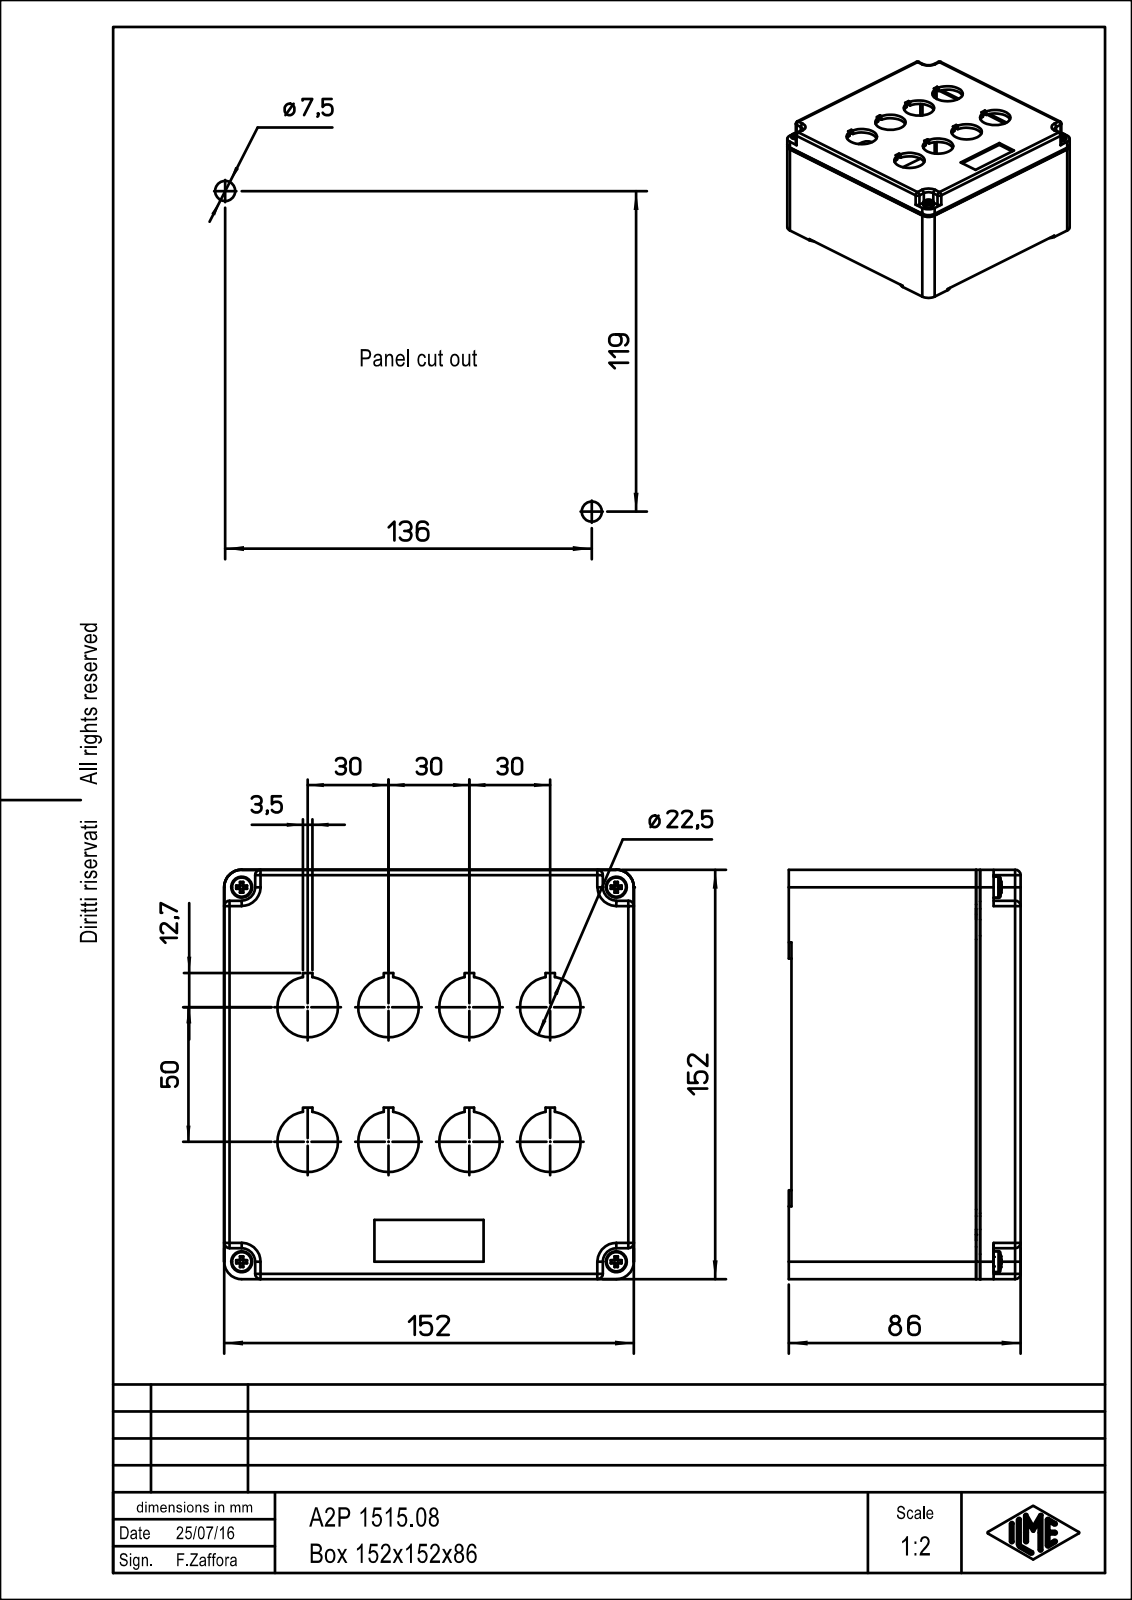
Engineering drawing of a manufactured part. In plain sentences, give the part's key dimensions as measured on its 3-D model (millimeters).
The part is named "COVER; BOX; A2P_1515.08". Its 3-D file was written by "PTC Creo Elements/Direct Modeling 19.0B 21-Mar-2015 (C) Parametric Technology GmbH (AUTOMOTIVE_DESIGN)". It is 2 solids with 1028 faces: 811 planar, 177 cylindrical and 40 other. Overall it measures 152.02 by 152 by 86 millimeters. Its volume is 382 133 cubic millimeters and its surface area 200 962 square millimeters. Round holes: 8 of diameter 22.5, 6 of diameter 3.3, 4 of diameter 4.5, 2 of diameter 5.8, 2 of diameter 7.5, 1 of diameter 10.6, 1 of diameter 10.61. Round bosses or shafts: 4 of diameter 7.8, 4 of diameter 4, 2 of diameter 6.2, 2 of diameter 6, 1 of diameter 7. Partial cylindrical surfaces (rounded edges, fillets, slot ends): 22 of radius 0.33, 17 of radius 2, 12 of radius 6, 12 of radius 6.5, 6 of radius 5, 6 of radius 8, 4 of radius 0.27, 4 of radius 0.27. The main face-to-face distances are 3, 82, 152, 85, 79, 4.38, 147.63, 147.62, 4.37, 143.25. The hole center spacings are 139, 30, 58.31, 95.5, 122.84, 196.58, 50, 50.8.
